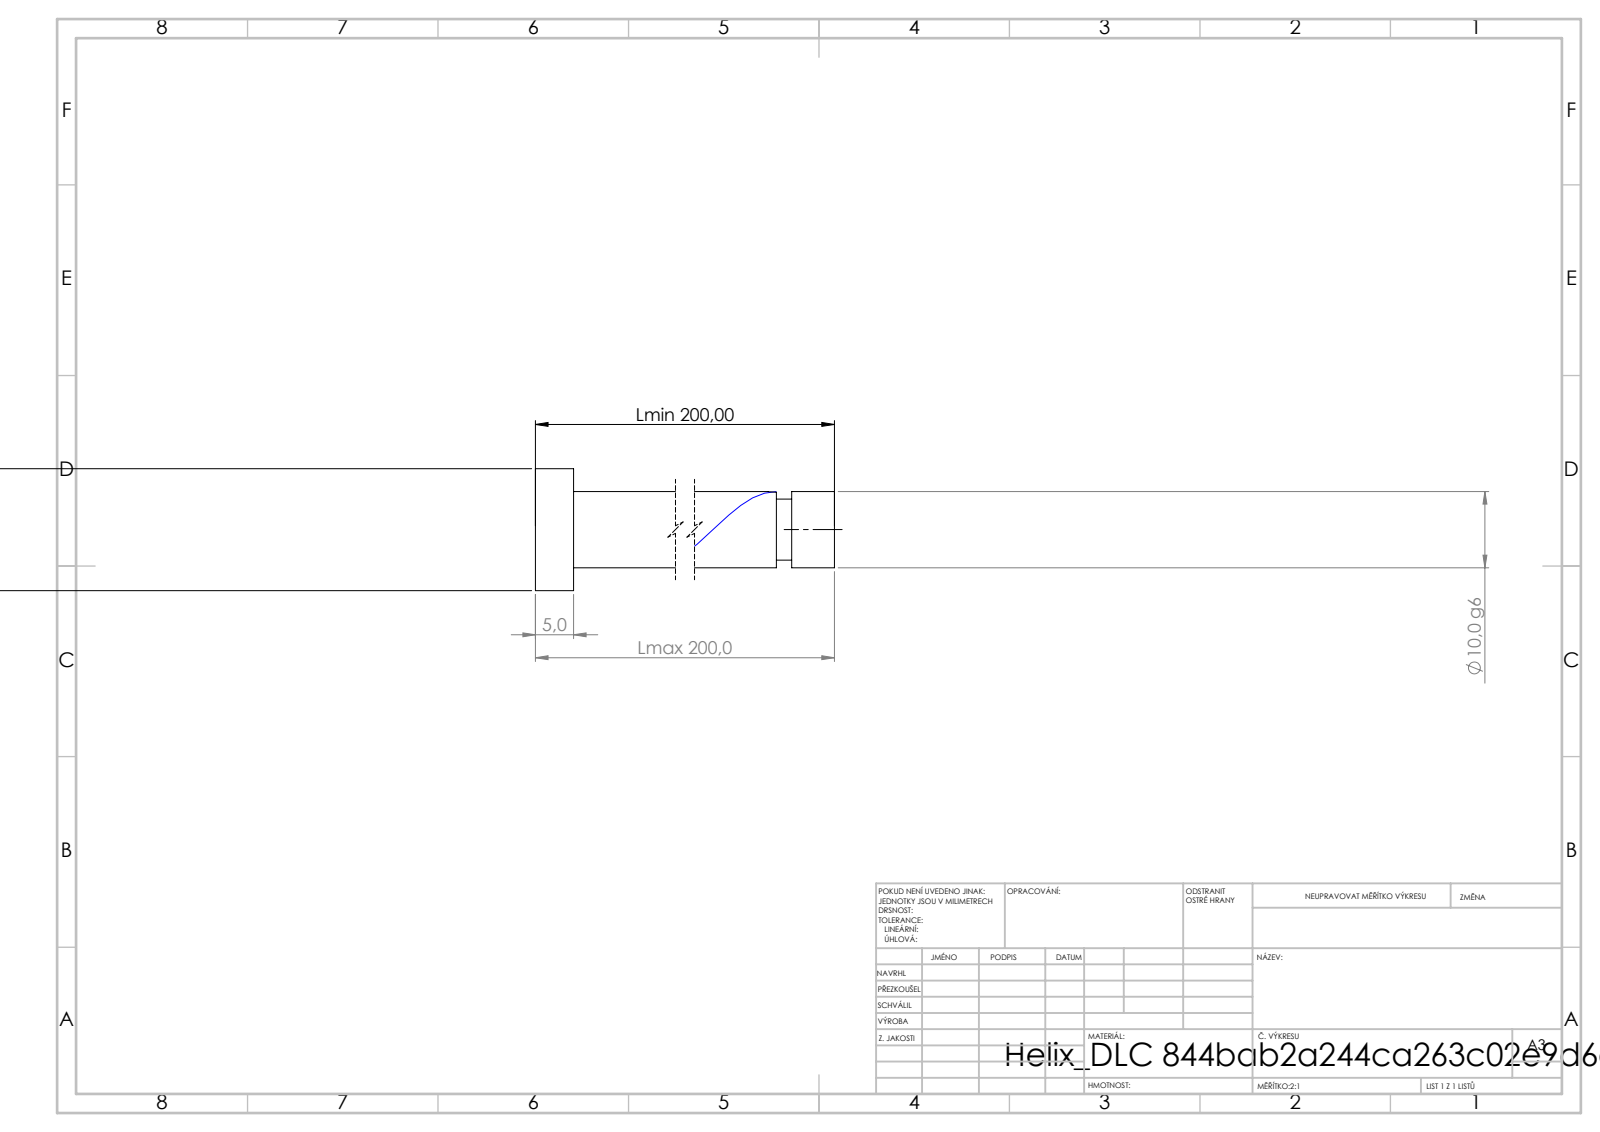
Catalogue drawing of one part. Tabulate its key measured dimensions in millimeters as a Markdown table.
| quantity | value |
| --- | --- |
| STEP written by | SolidWorks 2019 (CONFIG_CONTROL_DESIGN) |
| units | millimeters |
| bodies | 1 solid, 21 faces (6 planar, 14 cylindrical, 1 other) |
| overall size | 200 × 16 × 16 |
| volume | 16 114 mm³ |
| surface area | 6 971 mm² |
| round bosses / shafts (diameter × count) | 16 × 1, 10 × 1, 8 × 1 |
| main face-to-face distances | 5, 200, 195, 194.39, 189.39, 5.61, 192.39, 187.39, 2, 7.61 |
